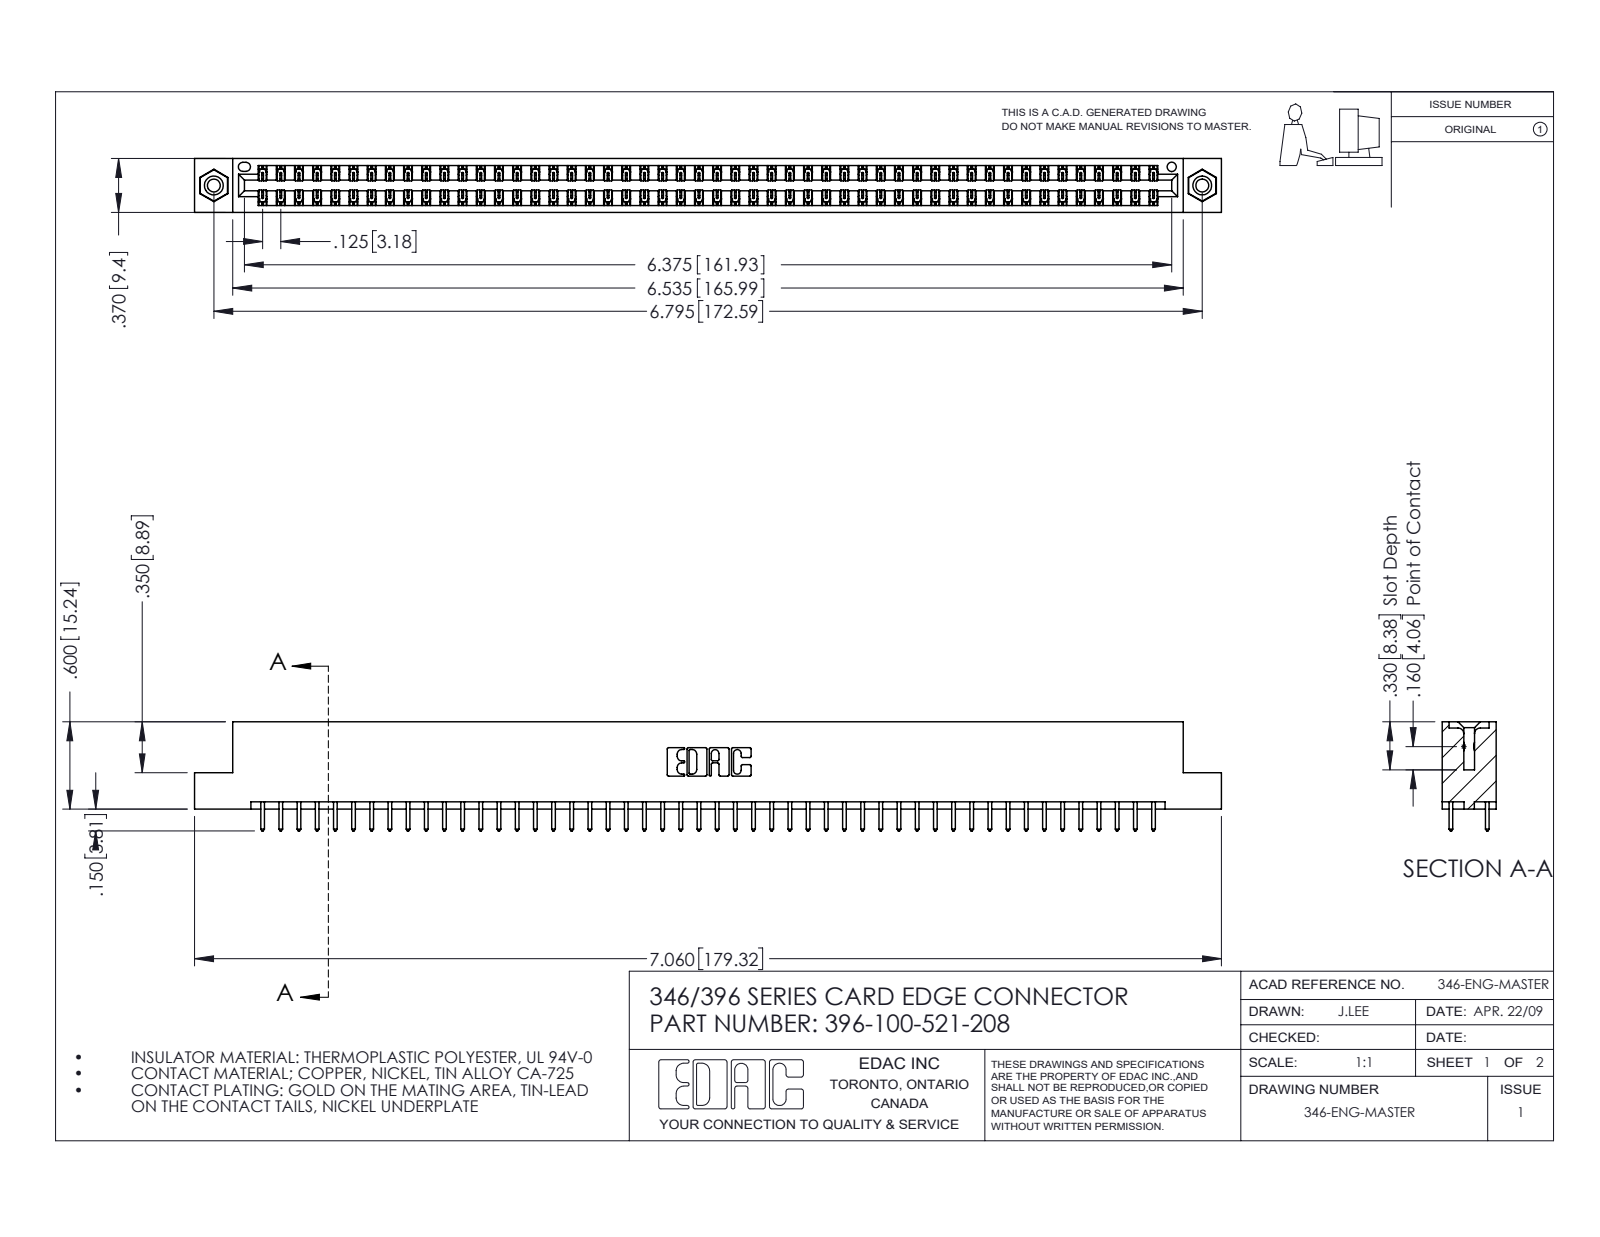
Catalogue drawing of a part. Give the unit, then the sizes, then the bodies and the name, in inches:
Units: inches
Overall size (bounding box): 7.06 × 0.75 × 0.37
Round holes (diameter × count): ⌀0.089 ×2, ⌀0.125 ×2, ⌀0.156 ×2, ⌀0.064 ×1
Round bosses / shafts (diameter × count): ⌀0.155 ×2
Partial cylindrical surfaces — rounded edges, fillets, slot ends (radius × count): R0.006 ×150, R0.01 ×100, R0.01 ×22, R0.007 ×6, R0.031 ×6, R0.026 ×3, R0.014 ×2, R0.022 ×2
Main face-to-face distances: 0.048, 0.322, 0.25, 0.37, 0.072, 0.298, 0.025, 0.275, 0.148, 0.222
Hole centre spacings: 0.246, 6.586, 6.795
Volume: 1.068 in³ · Surface area: 37.09 in²
Bodies: 103 solids, 5382 faces (3608 planar, 1758 cylindrical, 16 other)
Part name (STEP PRODUCT): 396-100-521-208; 345-292-001_345-293-121; 346 Part_Flush Mounting Lugs - 0.156 Dia-TI; 345-250-001_345-250-003-102
STEP written by: SolidWorks 2016 (CONFIG_CONTROL_DESIGN)
